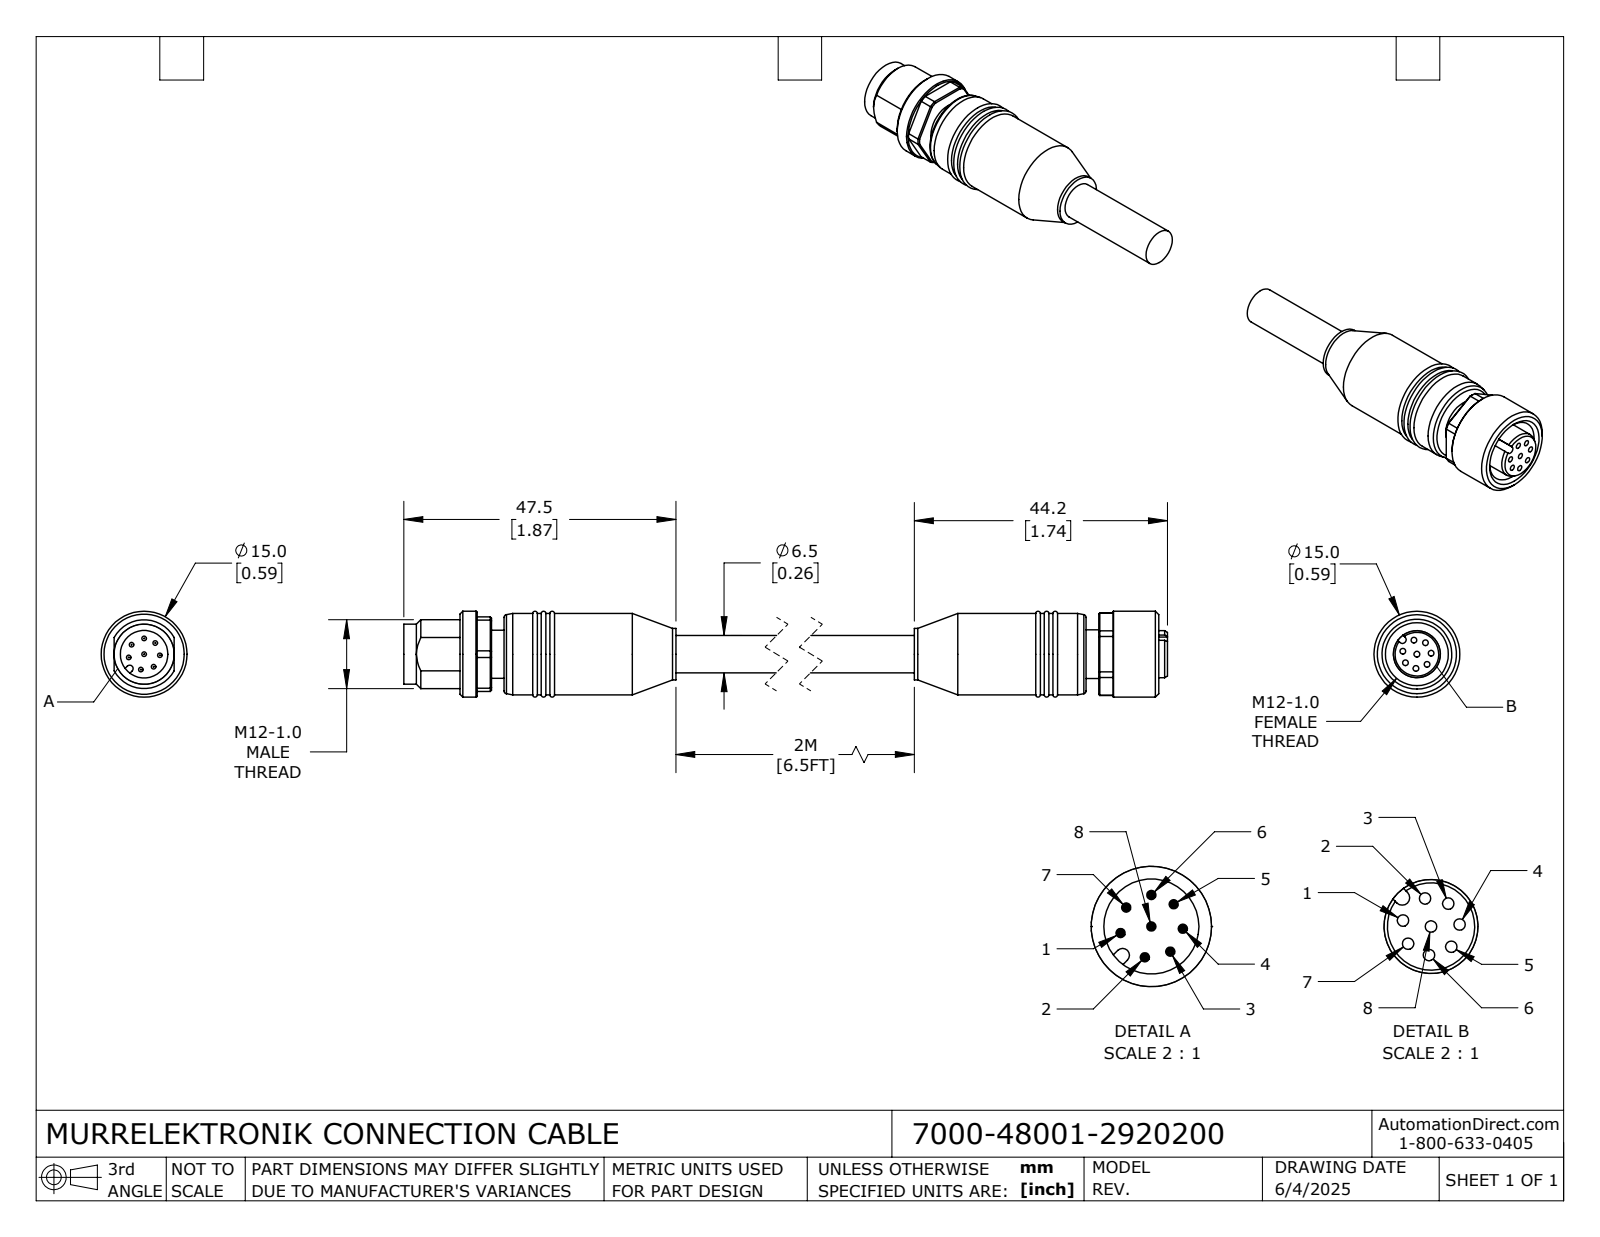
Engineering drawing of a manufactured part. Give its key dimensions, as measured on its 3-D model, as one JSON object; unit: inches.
{"part_name": "7000-48001-2920200_FEMALE; 7000-48001-2920200_MALE; 7000-48001-2920200", "step_written_by": "SolidWorks 2024 (CONFIG_CONTROL_DESIGN)", "units": "inches", "bodies": {"solids": 2, "faces": 222, "planar": 64, "cylindrical": 89, "other": 69}, "overall_size": [6.169, 0.591, 0.591], "volume_in3": 0.806, "surface_area_in2": 10.25, "round_holes": [[0.039, 8], [0.327, 1], [0.433, 1]], "round_bosses_or_shafts": [[0.031, 8], [0.591, 1], [0.559, 1], [0.413, 1], [0.354, 1], [0.335, 1], [0.331, 1], [0.323, 1]], "partial_cylinders_radius": [[0.024, 1], [0.026, 1], [0.236, 1], [0.283, 1]], "face_to_face_distances": [0.087, 5.008, 0.512, 5.094, 0.413, 4.921, 5.311, 2.055, 3.039, 1.969], "hole_center_spacings": [0.098, 0.081, 0.149, 0.195, 0.082, 0.166, 0.189, 0.189]}
